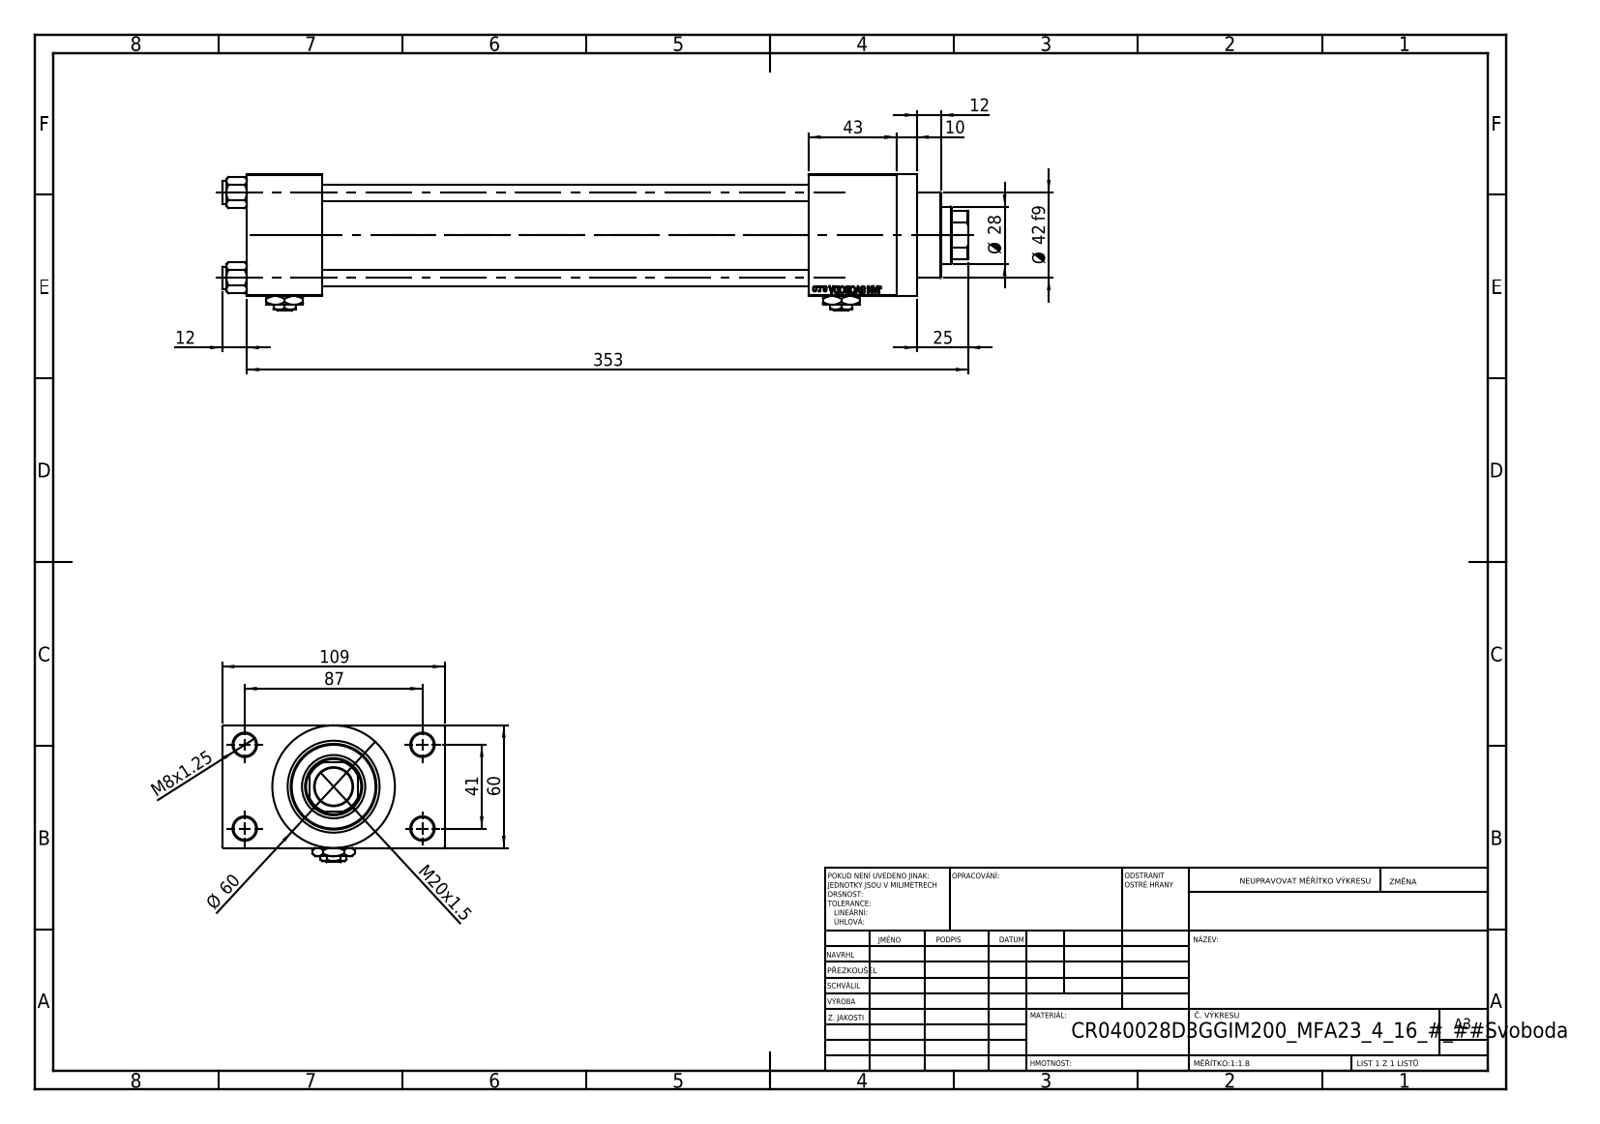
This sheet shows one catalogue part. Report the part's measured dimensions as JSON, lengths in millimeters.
{"part_name": "Zatka_pro_OIL_PORT; V215CR_D_Body; V215CR_VCP_D; NUT_M5_D (+2 more)", "step_written_by": "SolidWorks 2019 (CONFIG_CONTROL_DESIGN)", "units": "millimeters", "bodies": {"solids": 13, "faces": 1206, "planar": 546, "cylindrical": 100, "other": 560}, "overall_size": [365, 109, 67], "volume_mm3": 751920, "surface_area_mm2": 213036, "round_holes": [[8, 4], [11, 4], [7, 2], [16.66, 2], [24, 2], [18.5, 1], [28, 1], [31, 1], [40, 1], [45, 1]], "round_bosses_or_shafts": [[11, 4], [60, 1], [46, 1], [42, 1]], "partial_cylinders_radius": [[13.5, 1]], "face_to_face_distances": [60, 24.5, 84.5, 238, 37, 275, 318, 281, 43, 109], "hole_center_spacings": [22.65, 29.49, 41.7, 47.15, 48.09, 64.35, 76.49, 41]}
